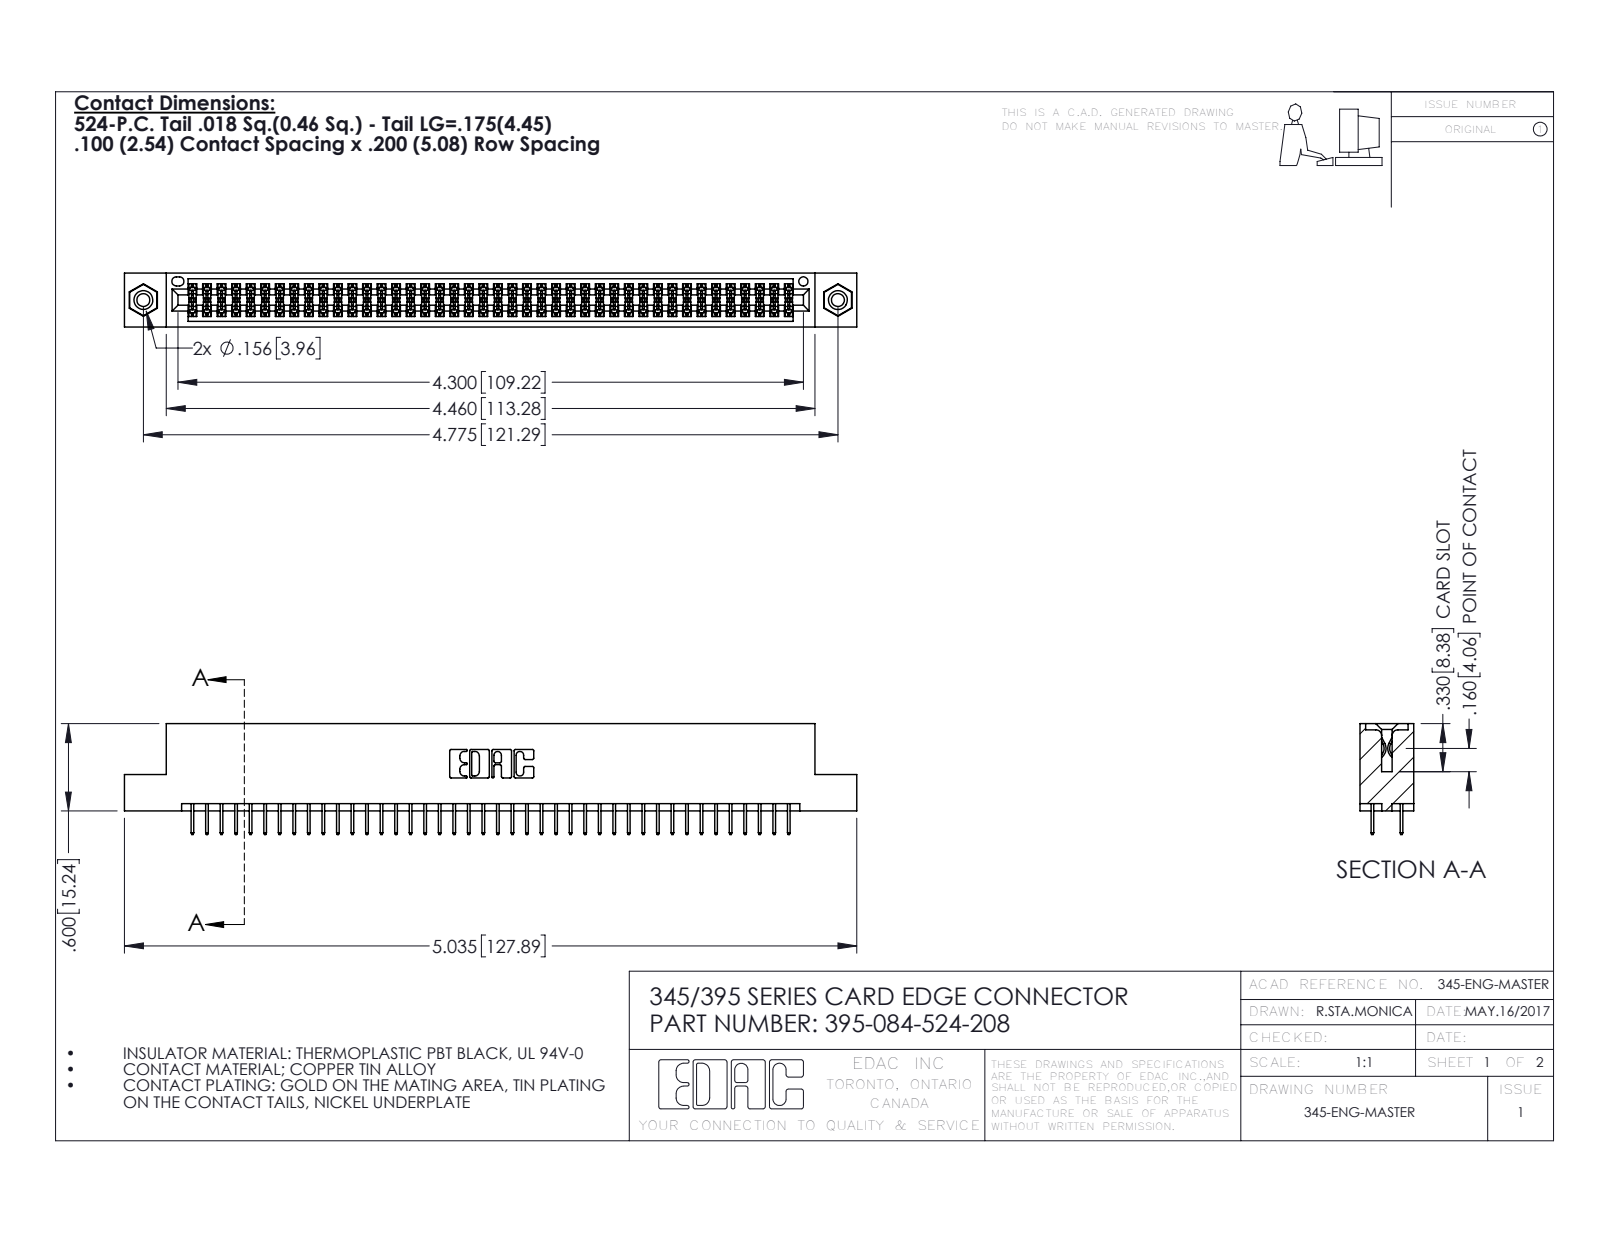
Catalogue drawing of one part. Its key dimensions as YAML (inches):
part_name: "345 Part_Flush Mounting Lugs - 0.156 Dia-TI; 345-250-001_345-250-003-102; 395-084-524-208; 345-292-001_345-293-124"
step_written_by: "SolidWorks 2016 (CONFIG_CONTROL_DESIGN)"
units: inches
bodies: {solids: 87, faces: 4722, planar: 3388, cylindrical: 1318, other: 16}
overall_size: [5.035, 0.762, 0.37]
volume: 0.75
surface_area: 27.66
round_holes:
  - {diameter: 0.089, count: 2}
  - {diameter: 0.125, count: 2}
  - {diameter: 0.156, count: 2}
  - {diameter: 0.064, count: 1}
round_bosses_or_shafts:
  - {diameter: 0.155, count: 2}
partial_cylinders:
  - {radius: 0.006, count: 126}
  - {radius: 0.01, count: 22}
  - {radius: 0.007, count: 6}
  - {radius: 0.031, count: 6}
  - {radius: 0.026, count: 3}
  - {radius: 0.014, count: 2}
  - {radius: 0.019, count: 2}
  - {radius: 0.022, count: 2}
face_to_face_distances: [0.072, 0.298, 0.2, 0.37, 0.098, 0.272, 0.025, 0.225, 0.072, 0.175]
hole_center_spacings: [0.27, 4.539, 4.775]
